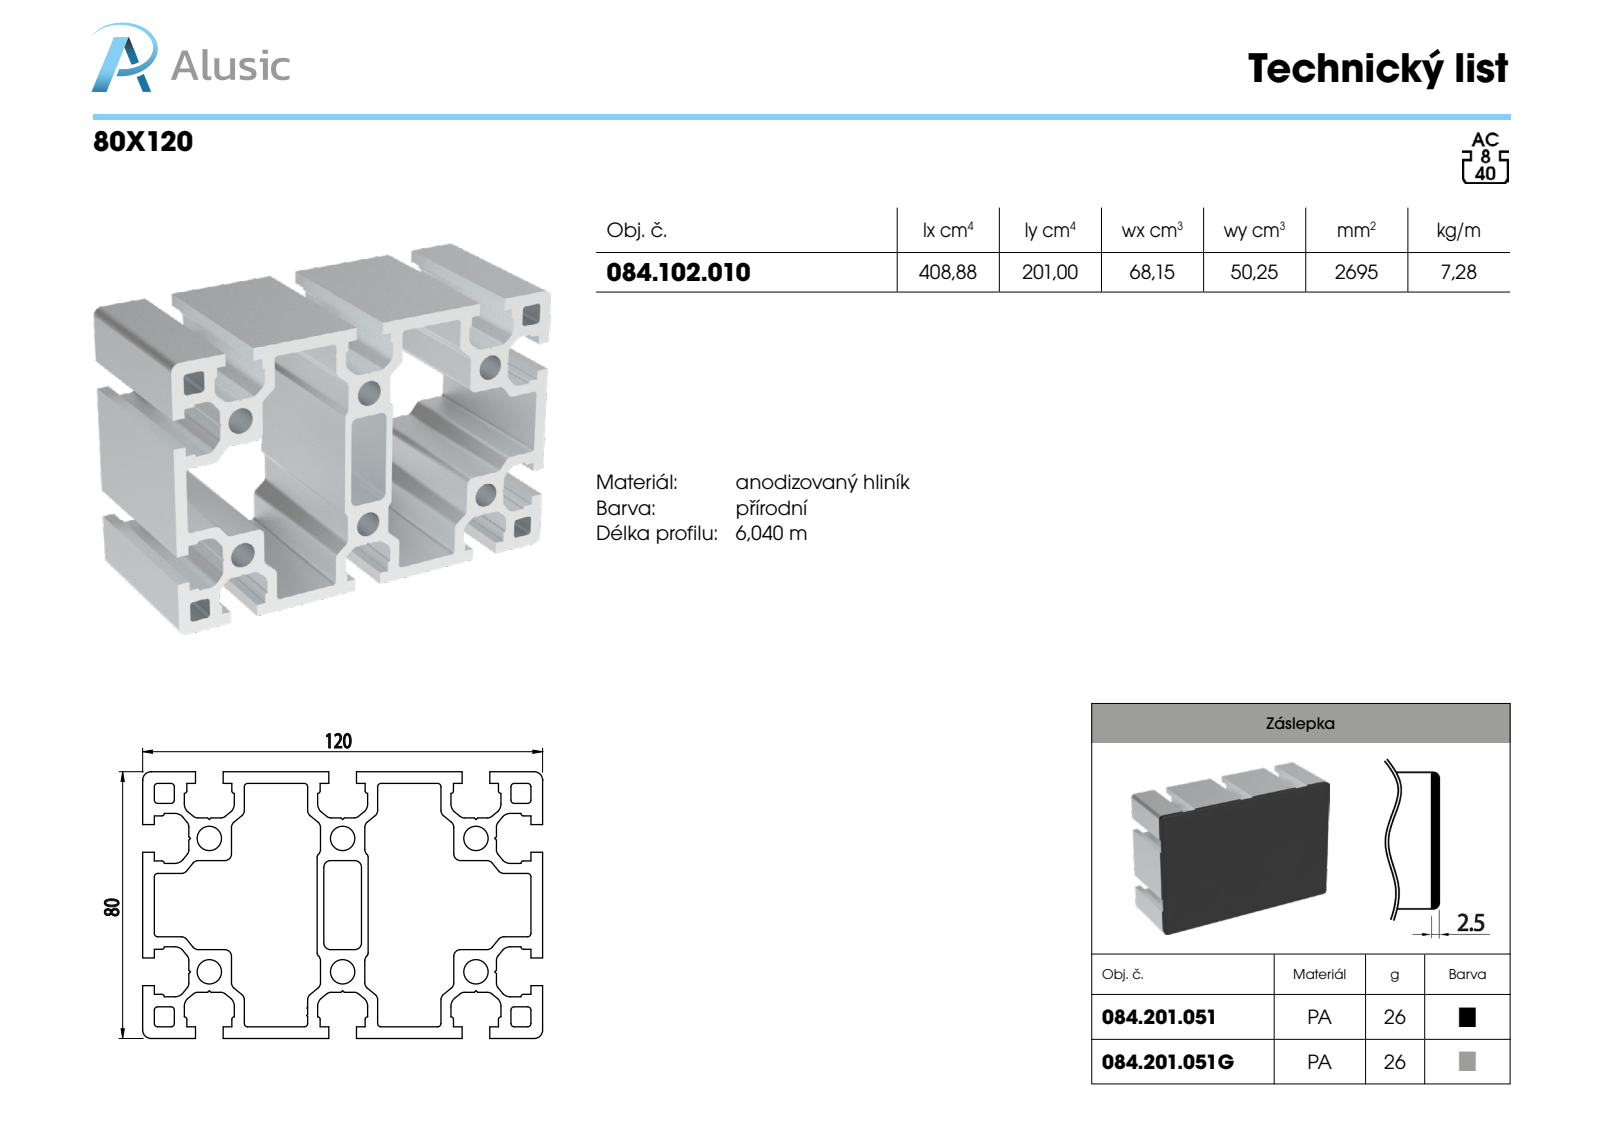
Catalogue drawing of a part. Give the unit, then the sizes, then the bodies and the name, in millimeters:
Units: millimetres
Overall size (bounding box): 120 × 80 × 10.5
Round holes (diameter × count): ⌀3.8 ×4
Round bosses / shafts (diameter × count): ⌀5.8 ×4
Partial cylindrical surfaces — rounded edges, fillets, slot ends (radius × count): R2 ×4, R2.5 ×4, R3.65 ×4
Main face-to-face distances: 2.5, 1.2, 19.4, 20.6, 80, 60.6, 59.4, 40, 99.4, 100.6
Hole centre spacings: 67, 107, 126.25
Volume: 24 442 mm³ · Surface area: 21 303 mm²
Bodies: 1 solid, 164 faces (56 planar, 44 cylindrical, 64 other)
Part name (STEP PRODUCT): 084.201.051
STEP written by: SolidWorks 2011 (CONFIG_CONTROL_DESIGN)
